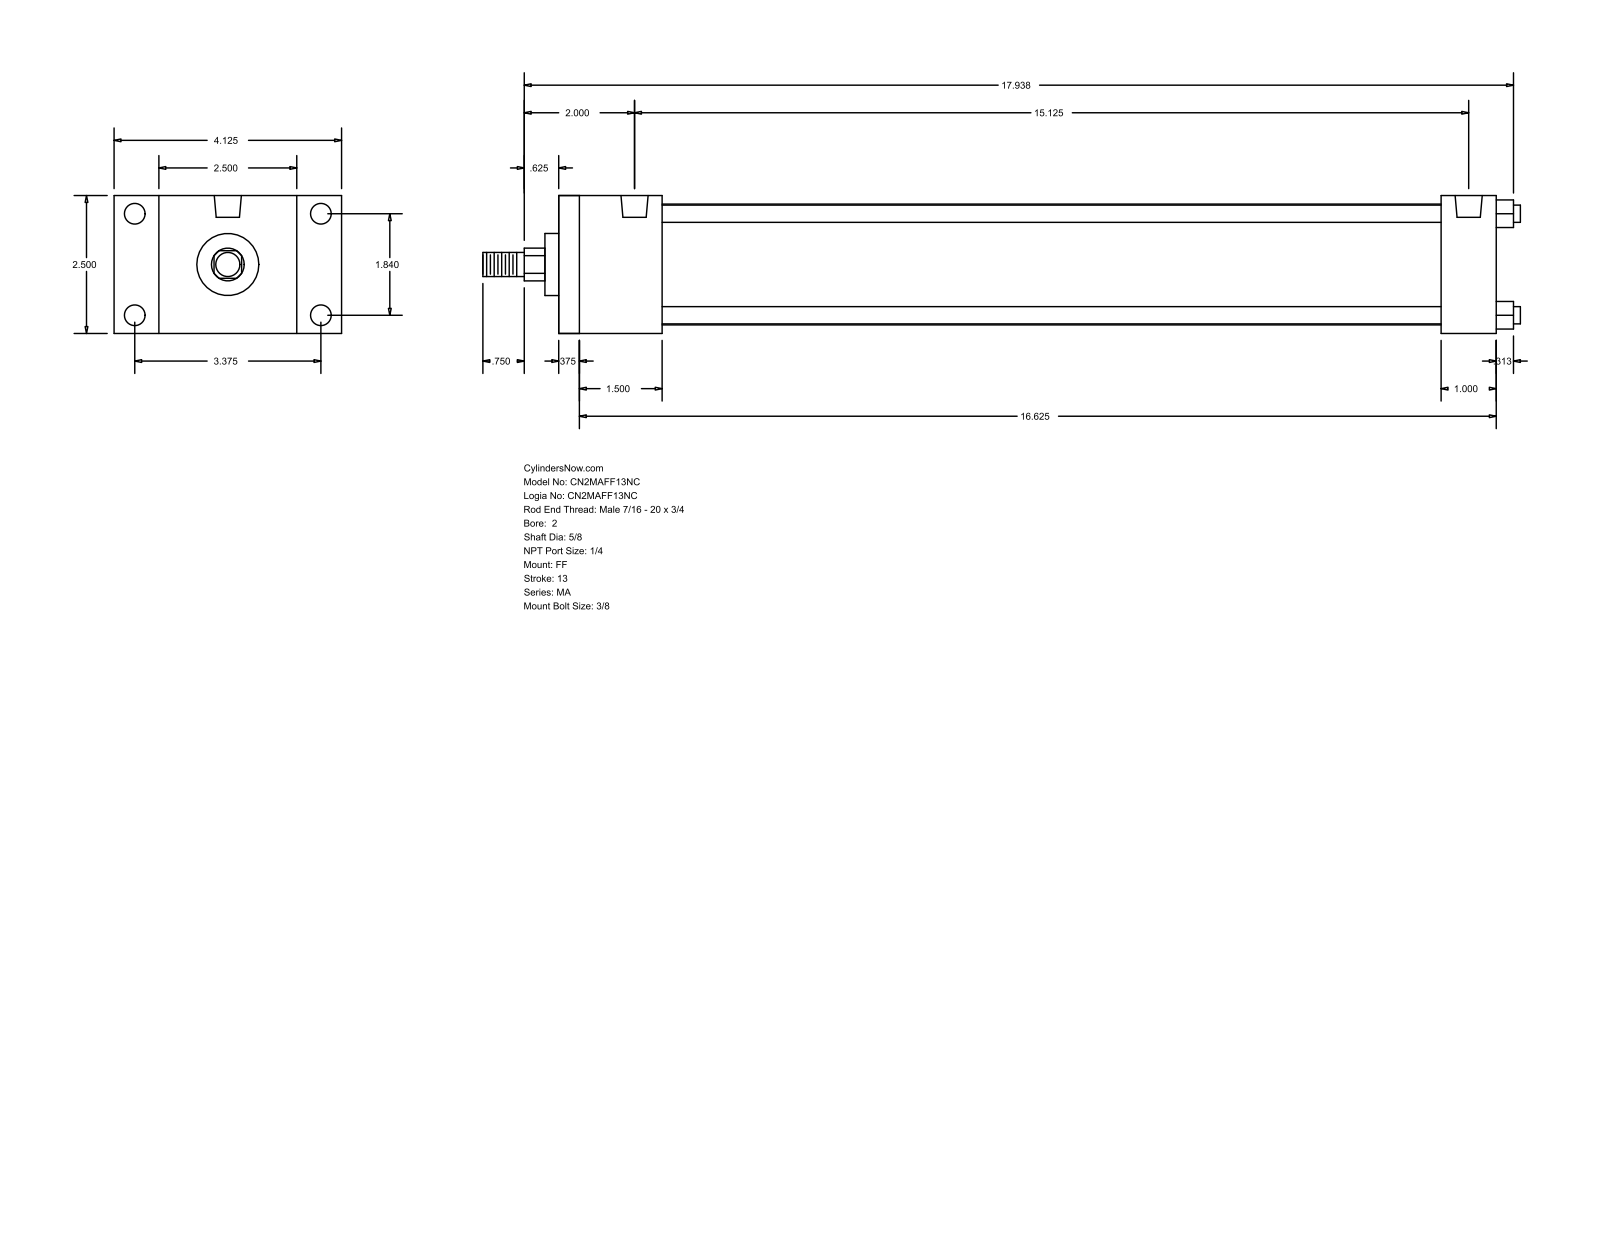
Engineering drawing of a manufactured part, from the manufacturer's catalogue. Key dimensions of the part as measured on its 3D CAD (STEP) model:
Part name (STEP PRODUCT): MA_FF__0200_0.625
STEP written by: GSSL Pune (CONFIG_CONTROL_DESIGN)
Units: millimetres
Bodies: 0 solids, 92 faces (64 planar, 28 cylindrical, 0 other)
Overall size (bounding box): 477.84 × 104.78 × 63.5
Round holes (diameter × count): ⌀7.94 ×4, ⌀9.53 ×4, ⌀12.49 ×2
Round bosses / shafts (diameter × count): ⌀7.94 ×4, ⌀55.63 ×1, ⌀28.57 ×1, ⌀15.88 ×1, ⌀11.11 ×1
Partial cylindrical surfaces — rounded edges, fillets, slot ends (radius × count): R7.54 ×1
Main face-to-face distances: 63.5, 431.8, 9.52, 422.28, 38.1, 47.62, 406.39, 396.87, 358.77, 384.18
Hole centre spacings: 46.74, 85.72, 97.63, 384.18
